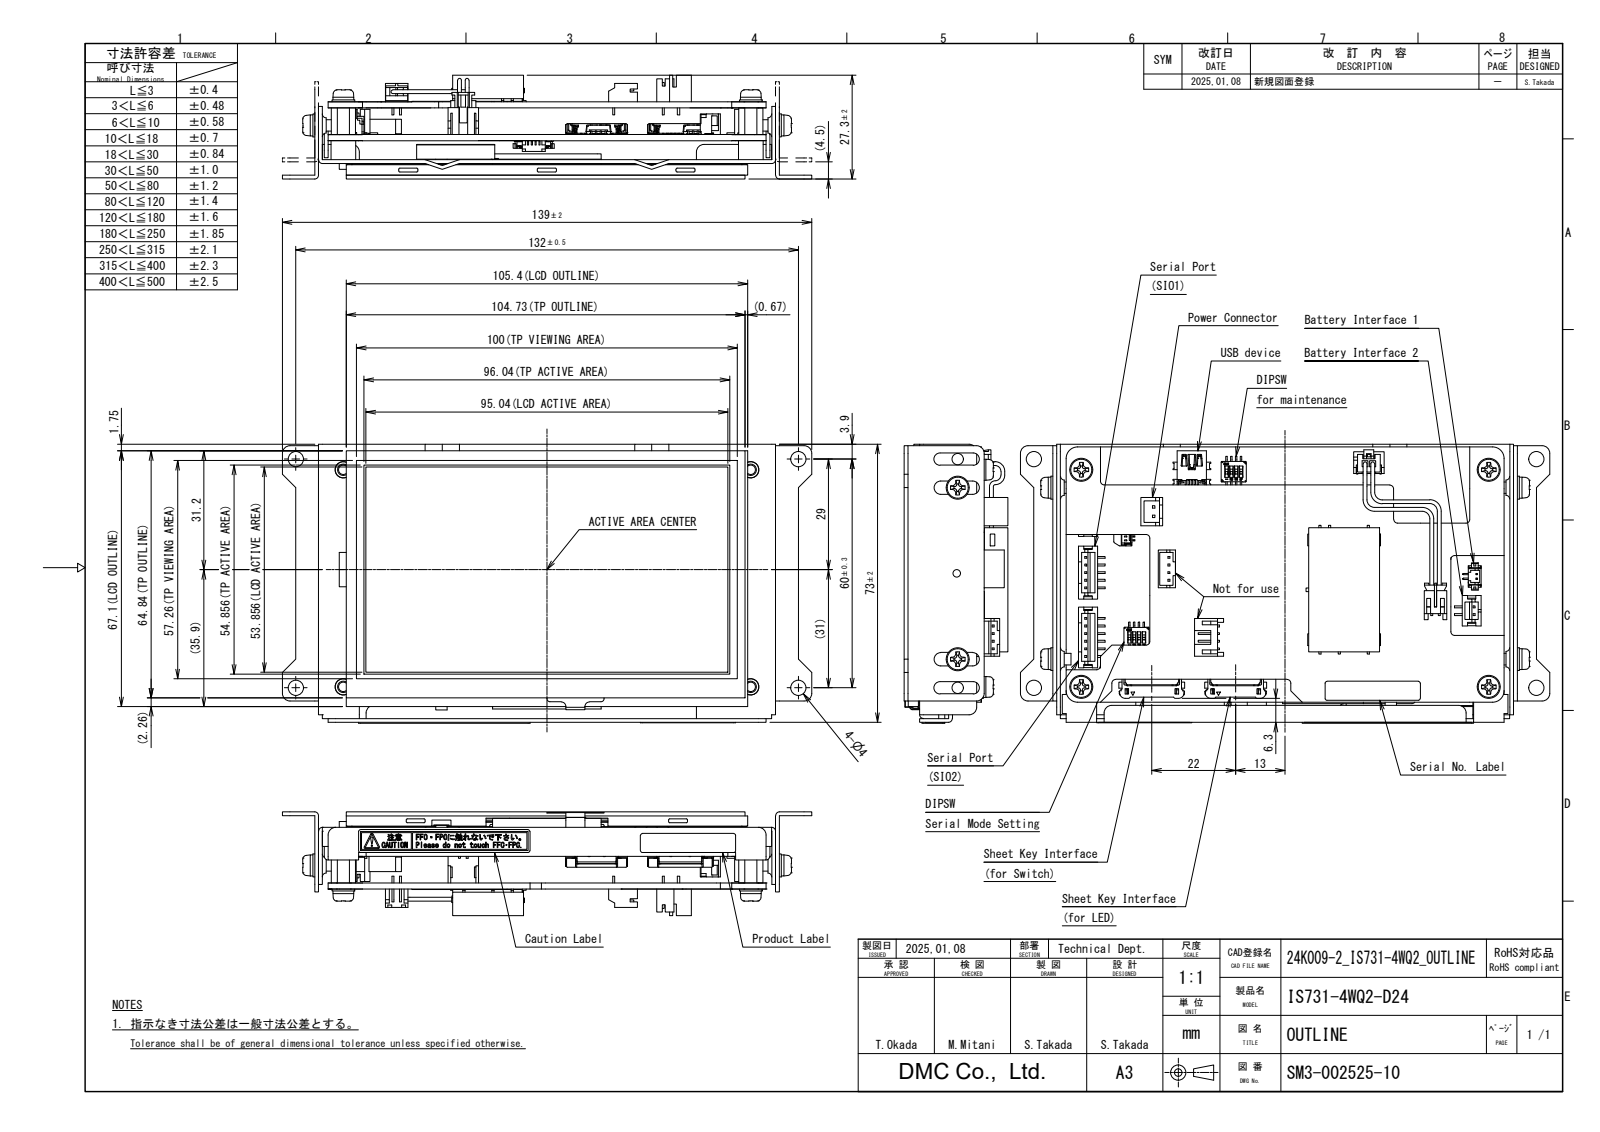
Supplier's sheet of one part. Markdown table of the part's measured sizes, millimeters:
| quantity | value |
| --- | --- |
| part name | HP_IS731-4WQ2-D24 |
| STEP written by | Autodesk Inventor 2020 (AUTOMOTIVE_DESIGN) |
| units | millimeters |
| bodies | 1 solid, 6539 faces (4960 planar, 930 cylindrical, 649 other) |
| overall size | 139 × 73.2 × 27.26 |
| volume | 72 816 mm³ |
| surface area | 102 240 mm² |
| round holes (diameter × count) | 4 × 6, 2.46 × 4, 3.5 × 4, 4.25 × 4, 1.2 × 2, 0.3 × 1, 1.33 × 1, 2 × 1 |
| round bosses / shafts (diameter × count) | 1 × 10, 3 × 8, 6 × 6, 5.5 × 6, 8 × 4, 6.5 × 4, 4.24 × 4, 3.7 × 3 |
| partial cylindrical surfaces (radius × count) | 0.1 × 116, 0.3 × 88, 0.2 × 50, 0.15 × 29, 1 × 28, 0.5 × 21, 2 × 20, 0.13 × 16 |
| main face-to-face distances | 1.6, 1.55, 9.01, 8.6, 17.61, 6.6, 11.66, 5.06, 1, 9.06 |
| hole center spacings | 12.5, 12.81, 57, 58.55, 60, 61.09, 107, 119.5 |
